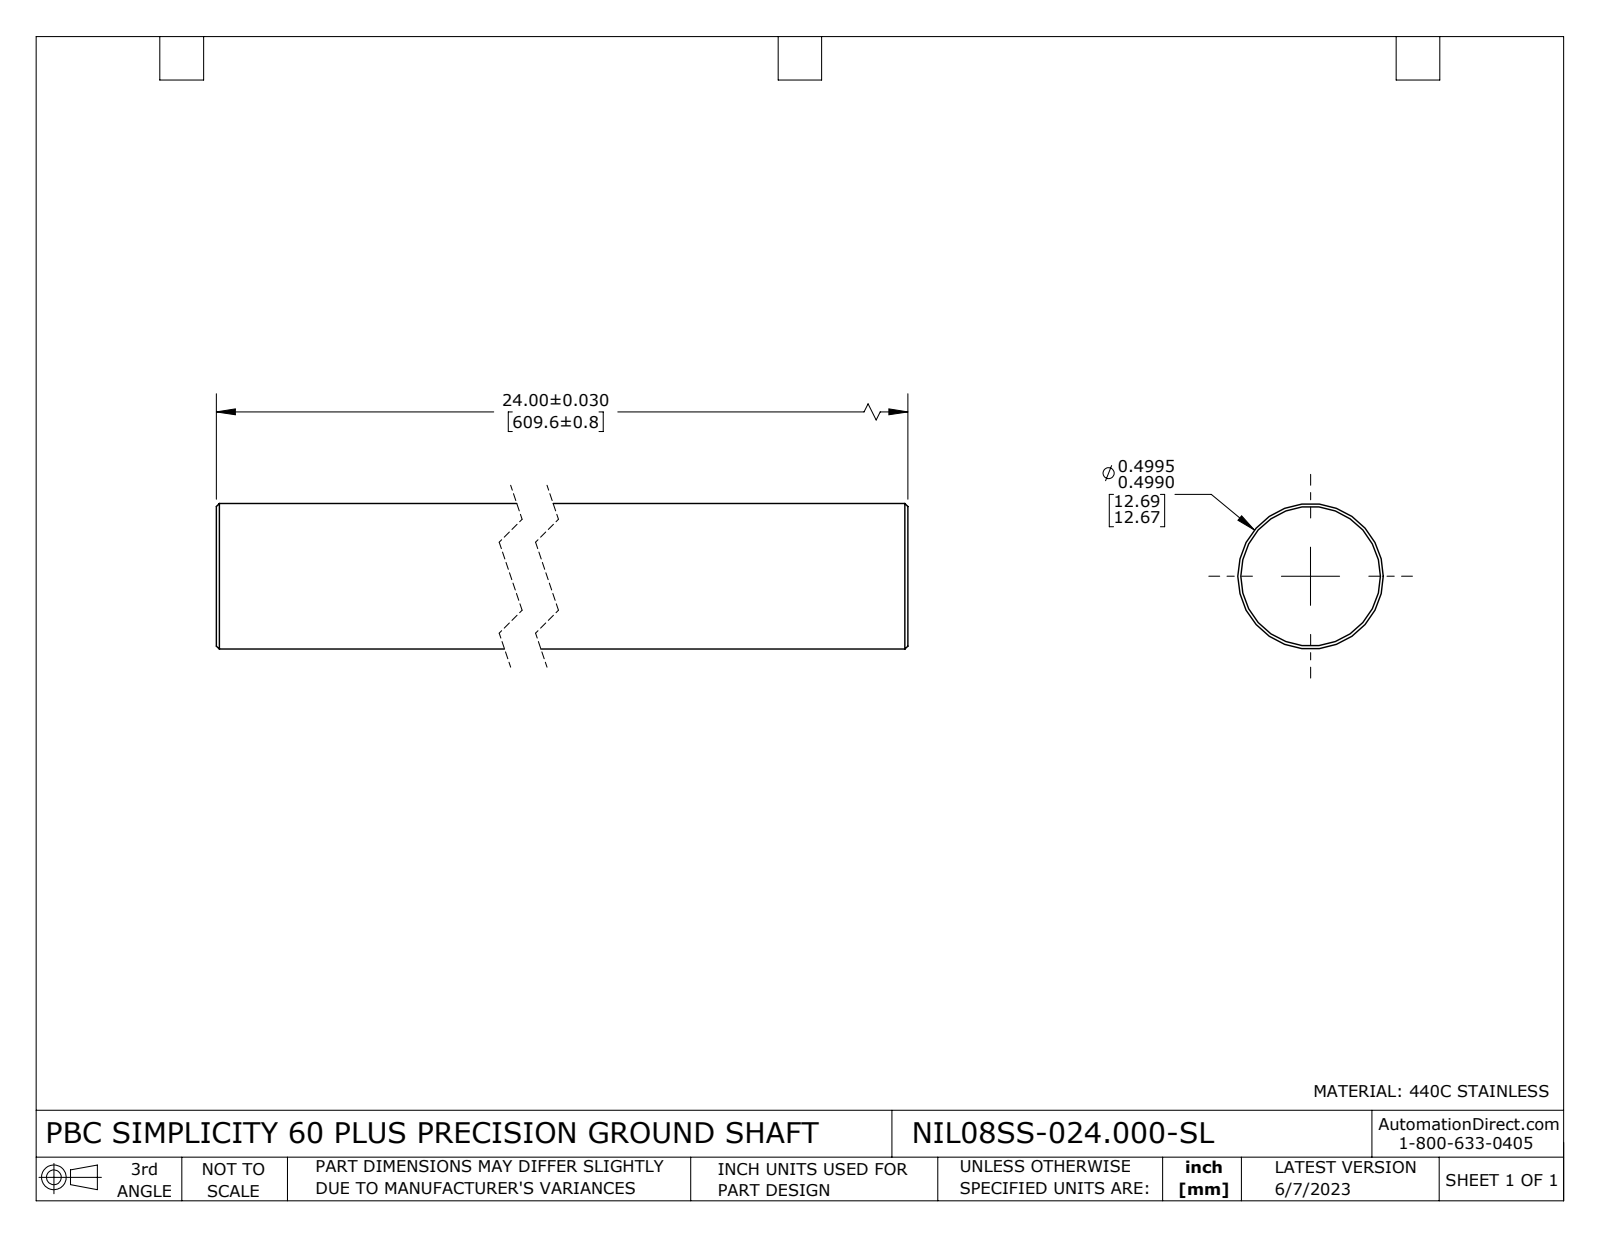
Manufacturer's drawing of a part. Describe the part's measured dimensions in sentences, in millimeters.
The part is named "NIL08SS-024.000-SL". Its 3-D file was written by "SolidWorks 2021 (CONFIG_CONTROL_DESIGN)". It is 1 solid with 8 faces: 2 planar, 2 cylindrical and 4 other. Overall it measures 609.6 by 12.7 by 12.7 millimeters. Its volume is 77 220 cubic millimeters and its surface area 24 560 square millimeters. Round bosses or shafts: 1 of diameter 12.7. The main face-to-face distances are 609.6.
